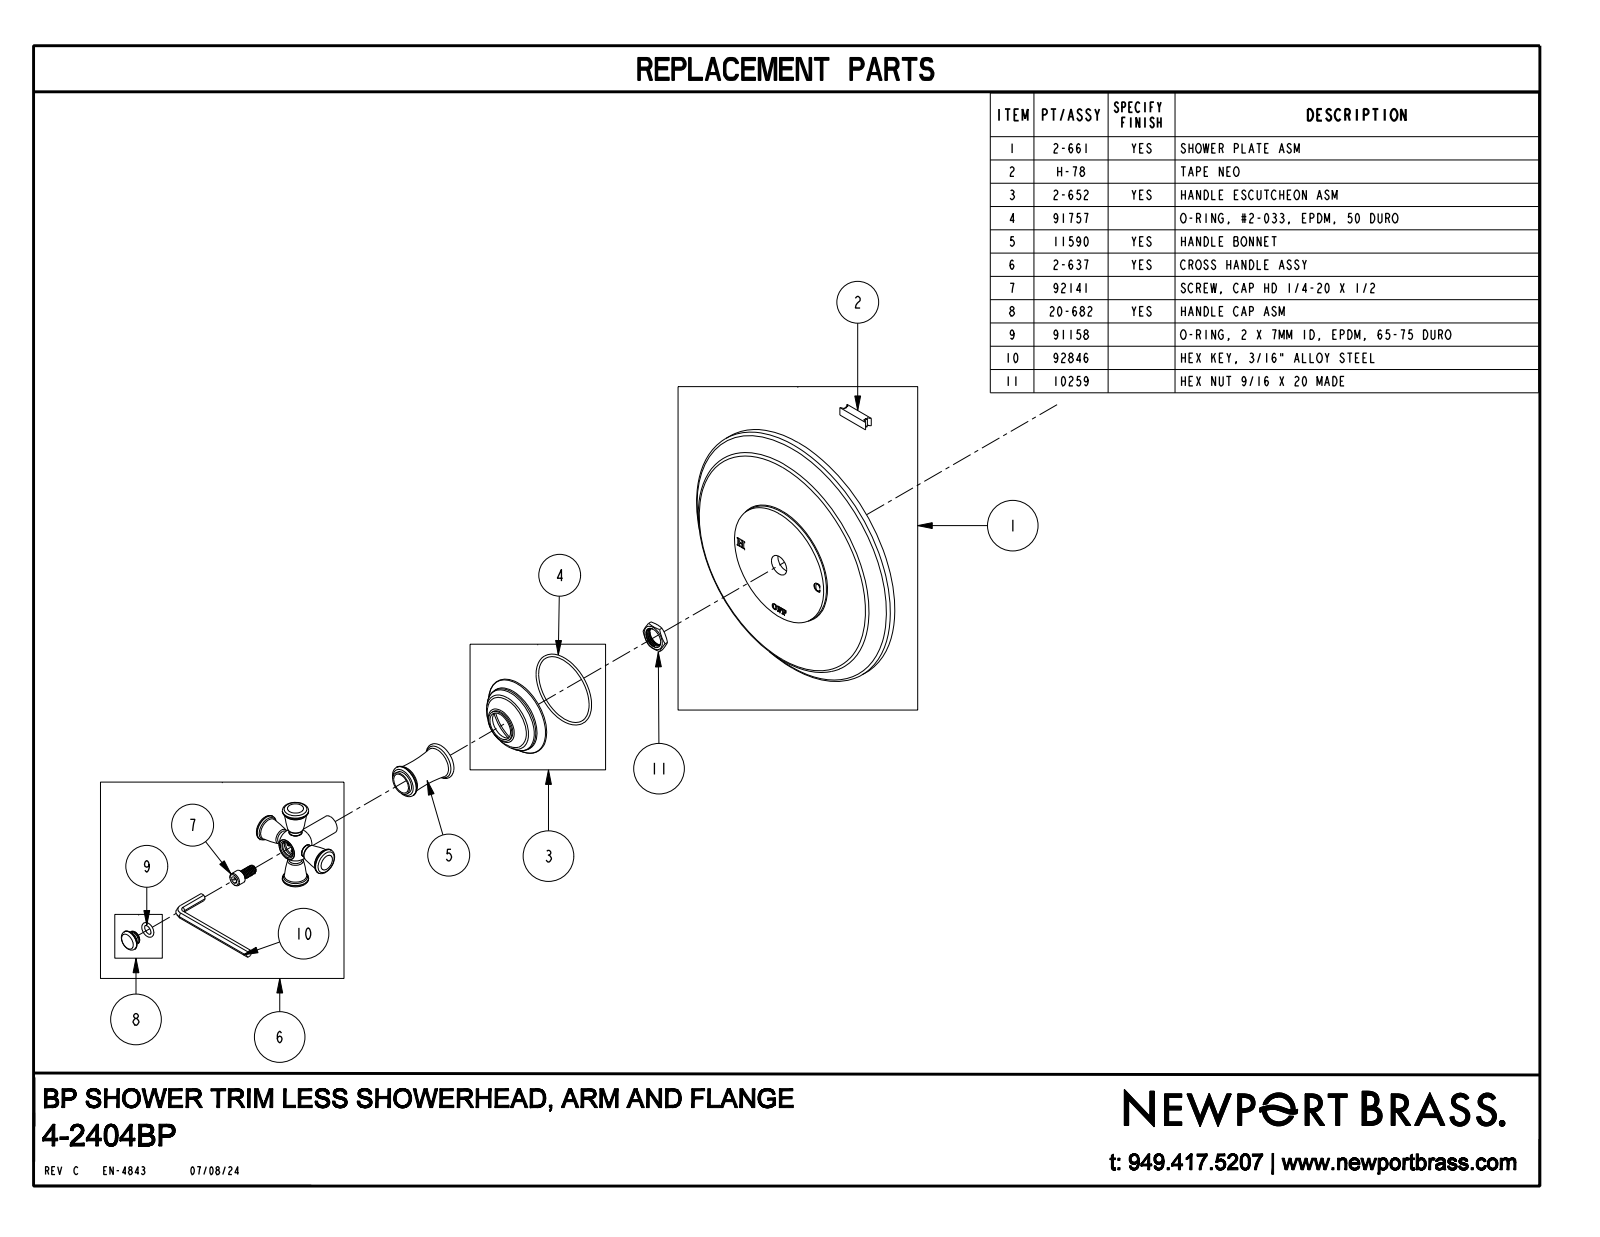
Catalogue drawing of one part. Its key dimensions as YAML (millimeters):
part_name: "4-2404BP"
step_written_by: "CREO PARAMETRIC BY PTC INC, 2018400 (CONFIG_CONTROL_DESIGN)"
units: millimeters
bodies: {solids: 1, faces: 270, planar: 39, cylindrical: 26, other: 205}
overall_size: [190.5, 190.5, 103.1]
volume: 481600
surface_area: 73480
round_bosses_or_shafts:
  - {diameter: 18.3, count: 2}
  - {diameter: 9.1, count: 2}
  - {diameter: 190.5, count: 1}
  - {diameter: 22.9, count: 1}
  - {diameter: 16.5, count: 1}
  - {diameter: 14.2, count: 1}
  - {diameter: 13.1, count: 1}
face_to_face_distances: [15.9, 19.1, 3.2, 73.4, 57.5, 54.4, 2, 75.4, 59.6, 56.4]
